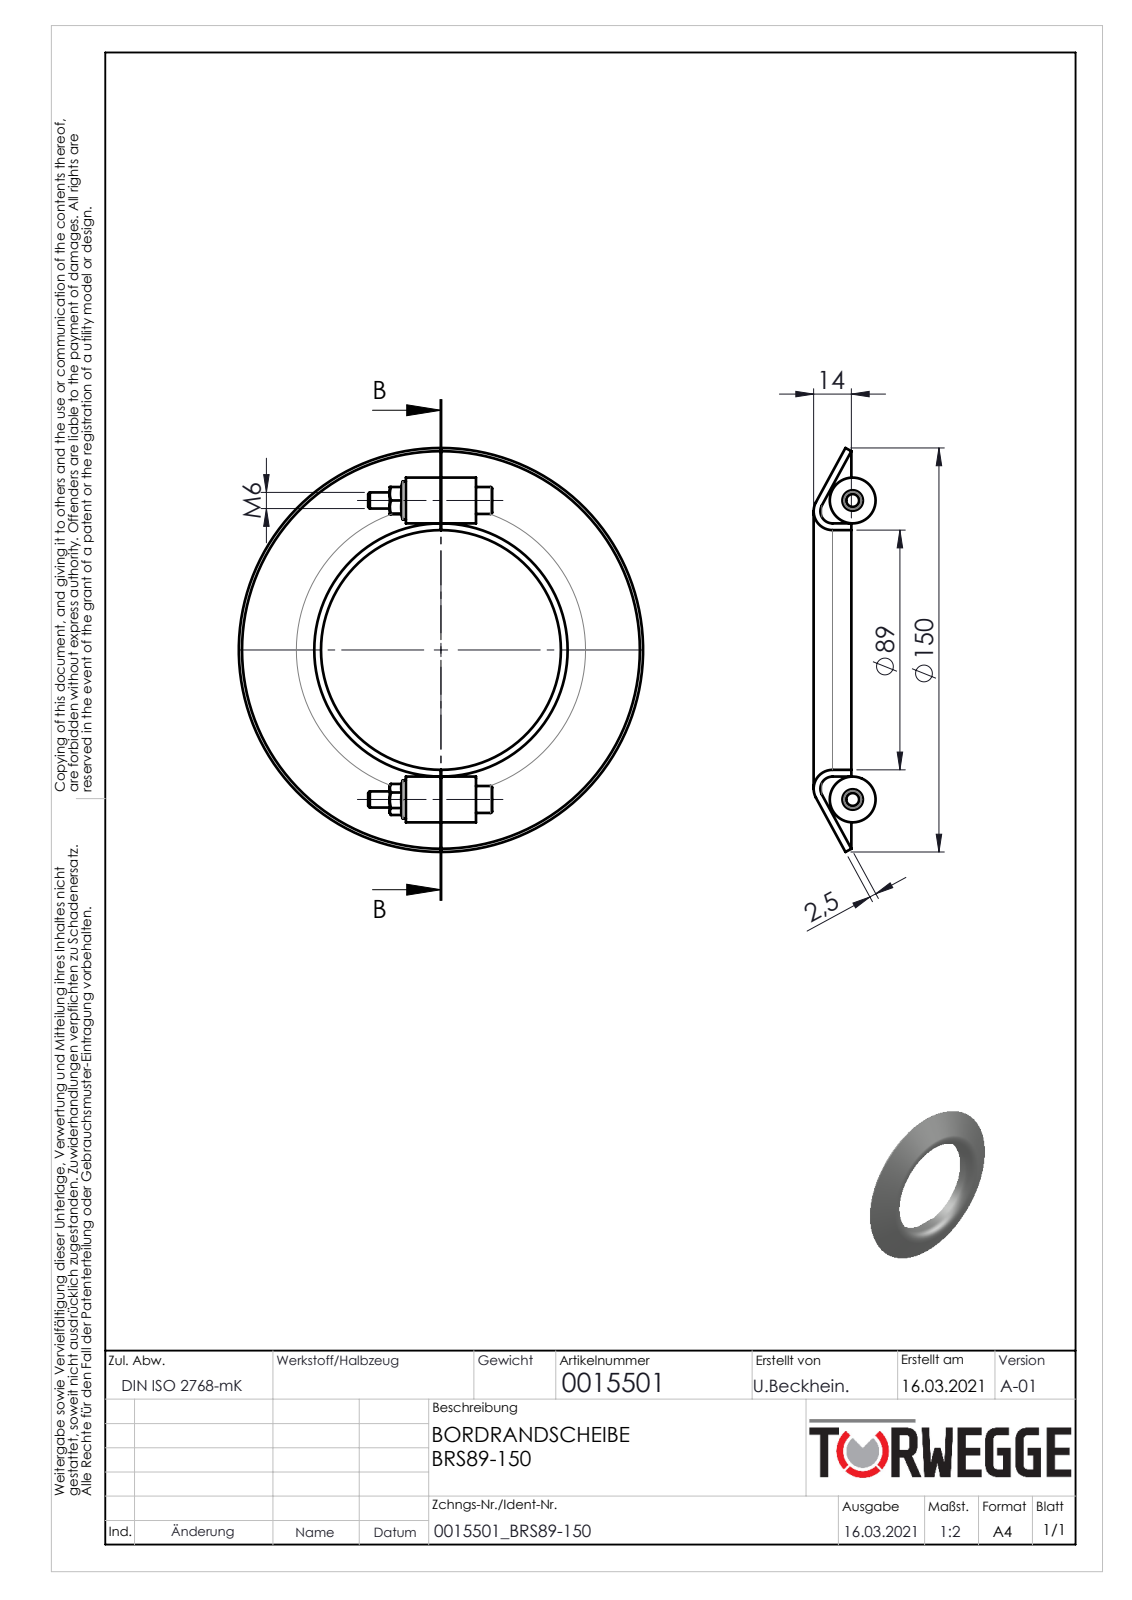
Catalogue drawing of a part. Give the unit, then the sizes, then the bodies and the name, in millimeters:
Units: millimetres
Overall size (bounding box): 150 × 150 × 22.99
Round holes (diameter × count): ⌀5 ×2, ⌀7.6 ×2, ⌀89 ×1
Round bosses / shafts (diameter × count): ⌀17 ×2, ⌀14.2 ×2, ⌀10 ×2, ⌀6 ×2, ⌀94 ×1
Main face-to-face distances: 13, 26, 6, 19, 32, 10, 38, 5, 8, 14
Hole centre spacings: 111
Volume: 50 862 mm³ · Surface area: 41 053 mm²
Bodies: 10 solids, 172 faces (60 planar, 36 cylindrical, 76 other)
Part name (STEP PRODUCT): 0015501
STEP written by: SolidWorks 2020 (AUTOMOTIVE_DESIGN)
